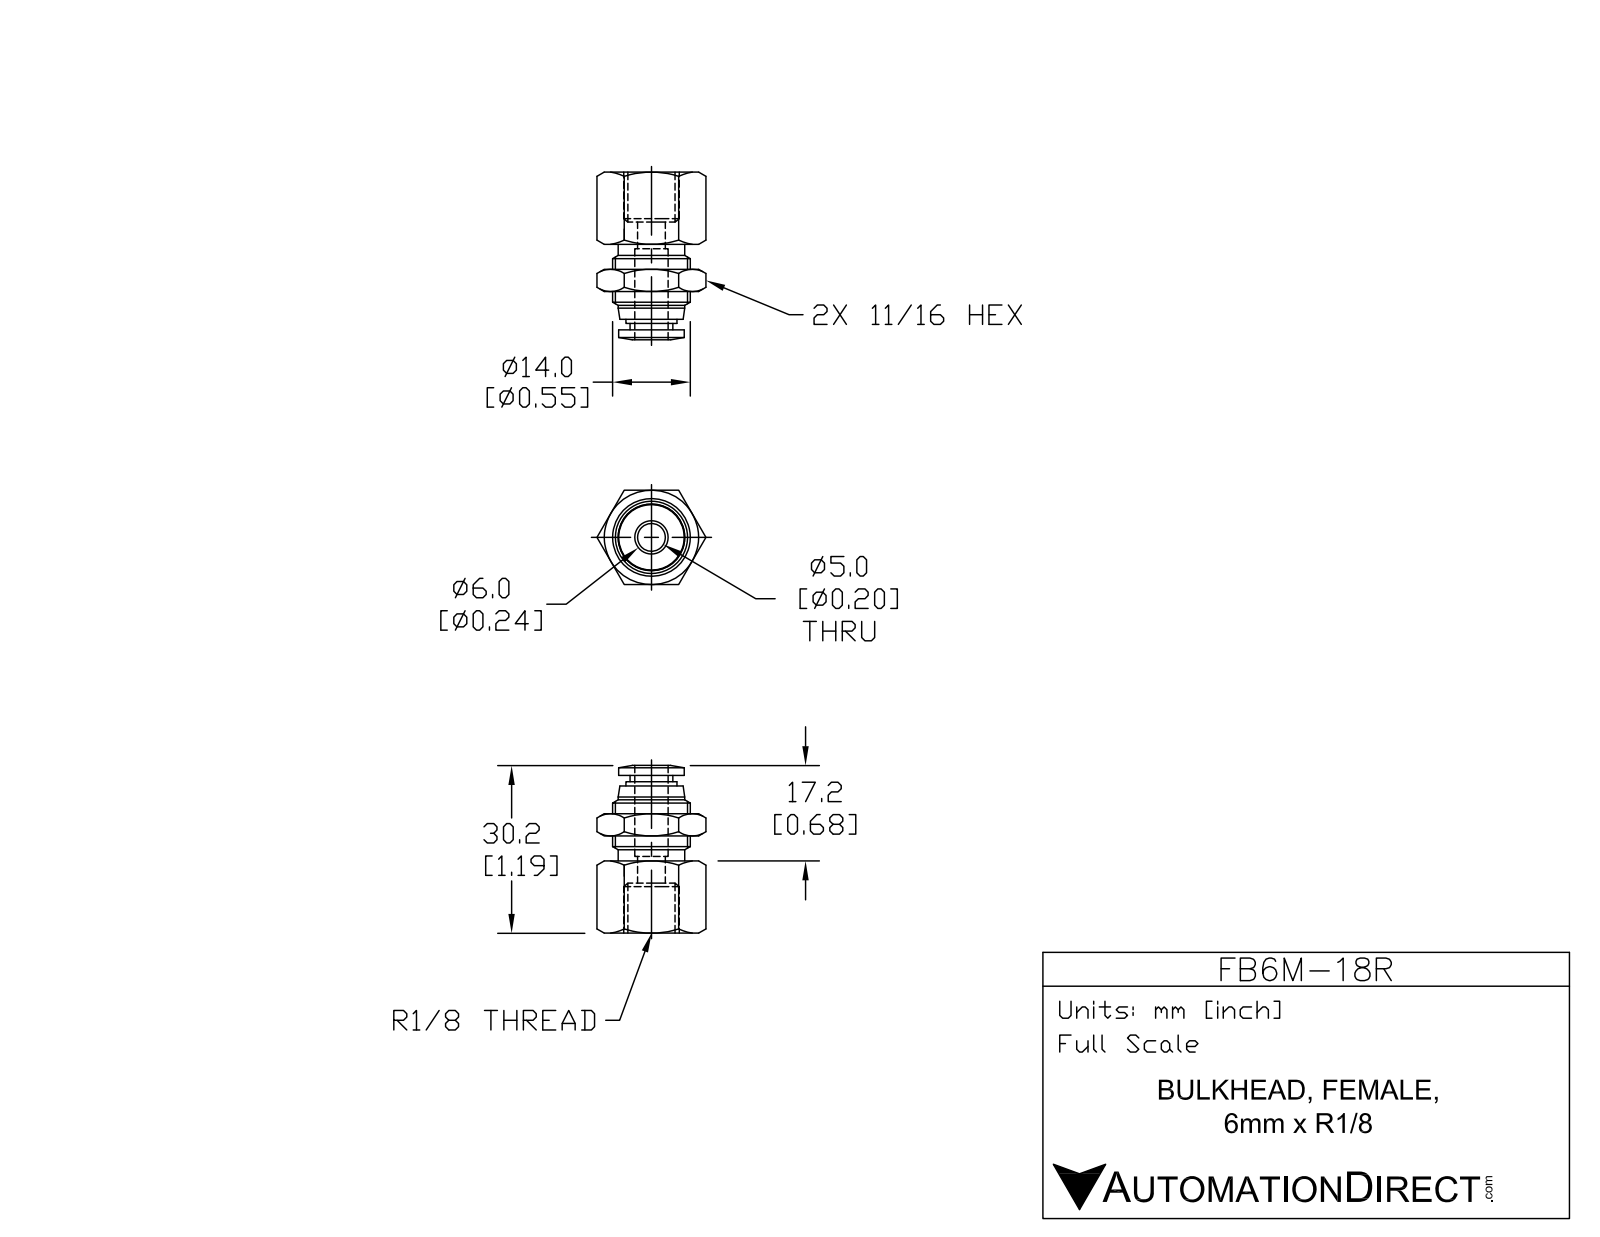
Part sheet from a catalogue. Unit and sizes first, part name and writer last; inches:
Units: inches
Overall size (bounding box): 1.189 × 0.773 × 0.669
Round holes (diameter × count): ⌀0.197 ×1, ⌀0.248 ×1
Round bosses / shafts (diameter × count): ⌀0.551 ×1, ⌀0.472 ×1, ⌀0.465 ×1, ⌀0.362 ×1, ⌀0.303 ×1
Main face-to-face distances: 0.669, 0.325, 0.157, 0.512, 0.837, 0.679, 0.167, 1.118, 0.606, 0.439
Volume: 0.276 in³ · Surface area: 4.516 in²
Bodies: 1 solid, 80 faces (22 planar, 18 cylindrical, 40 other)
Part name (STEP PRODUCT): FB6M-18R
STEP written by: SolidWorks 2015 (AUTOMOTIVE_DESIGN)
